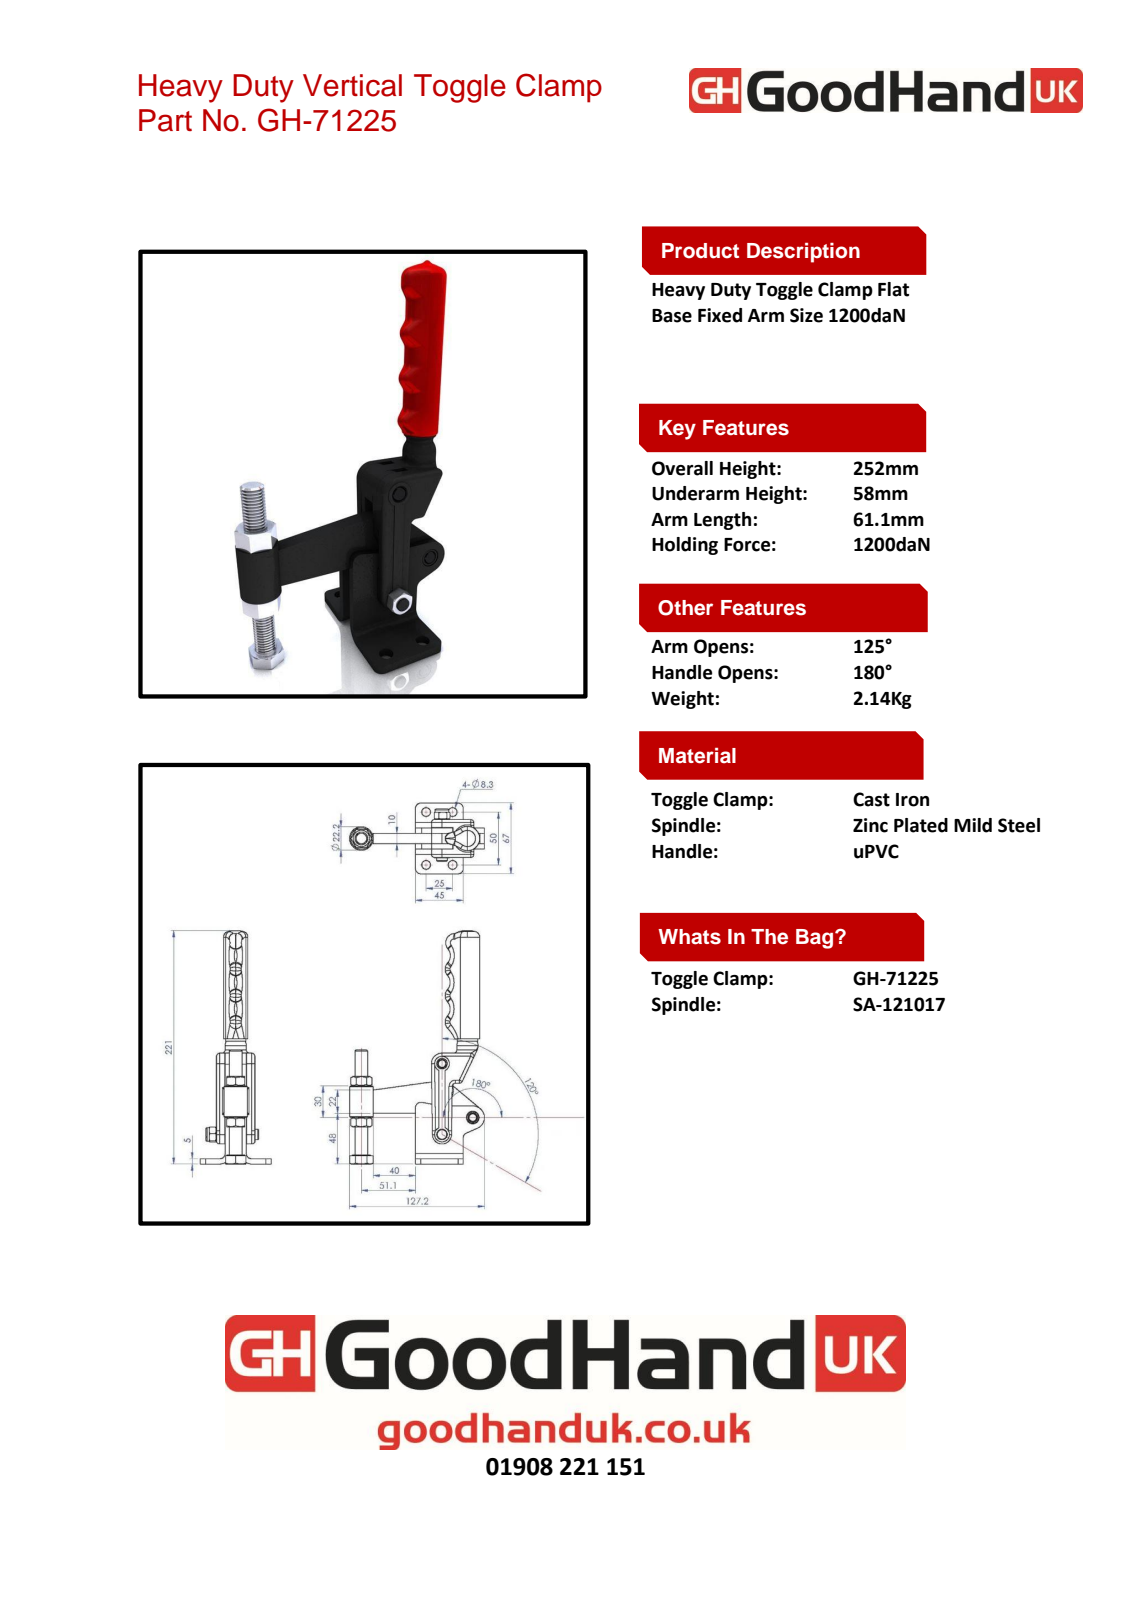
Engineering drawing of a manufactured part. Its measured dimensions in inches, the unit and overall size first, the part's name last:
Units: inches
Overall size (bounding box): 9.922 × 5.756 × 3.465
Round holes (diameter × count): ⌀0.276 ×4, ⌀0.327 ×4, ⌀0.402 ×1, ⌀0.472 ×1
Round bosses / shafts (diameter × count): ⌀0.709 ×3, ⌀0.875 ×1, ⌀0.874 ×1, ⌀0.866 ×1, ⌀0.472 ×1
Partial cylindrical surfaces — rounded edges, fillets, slot ends (radius × count): R1.181 ×7, R0.118 ×6, R0.197 ×6, R0.394 ×6, R0.354 ×4, R0.157 ×2, R0.472 ×2, R0.787 ×2
Main face-to-face distances: 0.236, 0.709, 0.472, 0.945, 0.242, 0.715, 0.951, 0.61, 0.368, 0.374
Hole centre spacings: 1.181, 2.362, 2.641, 3.038, 4.152, 1.339, 1.658, 1.774
Volume: 18.38 in³ · Surface area: 137.7 in²
Bodies: 6 solids, 306 faces (121 planar, 124 cylindrical, 61 other)
Part name (STEP PRODUCT): Group3^GH-71225(簡化)-1; Group4^GH-71225(簡化)-1; Group2^GH-71225(簡化)-1; Group1^GH-71225(簡化)-1 (+2 more)
STEP written by: SolidWorks 2016 (AUTOMOTIVE_DESIGN)
